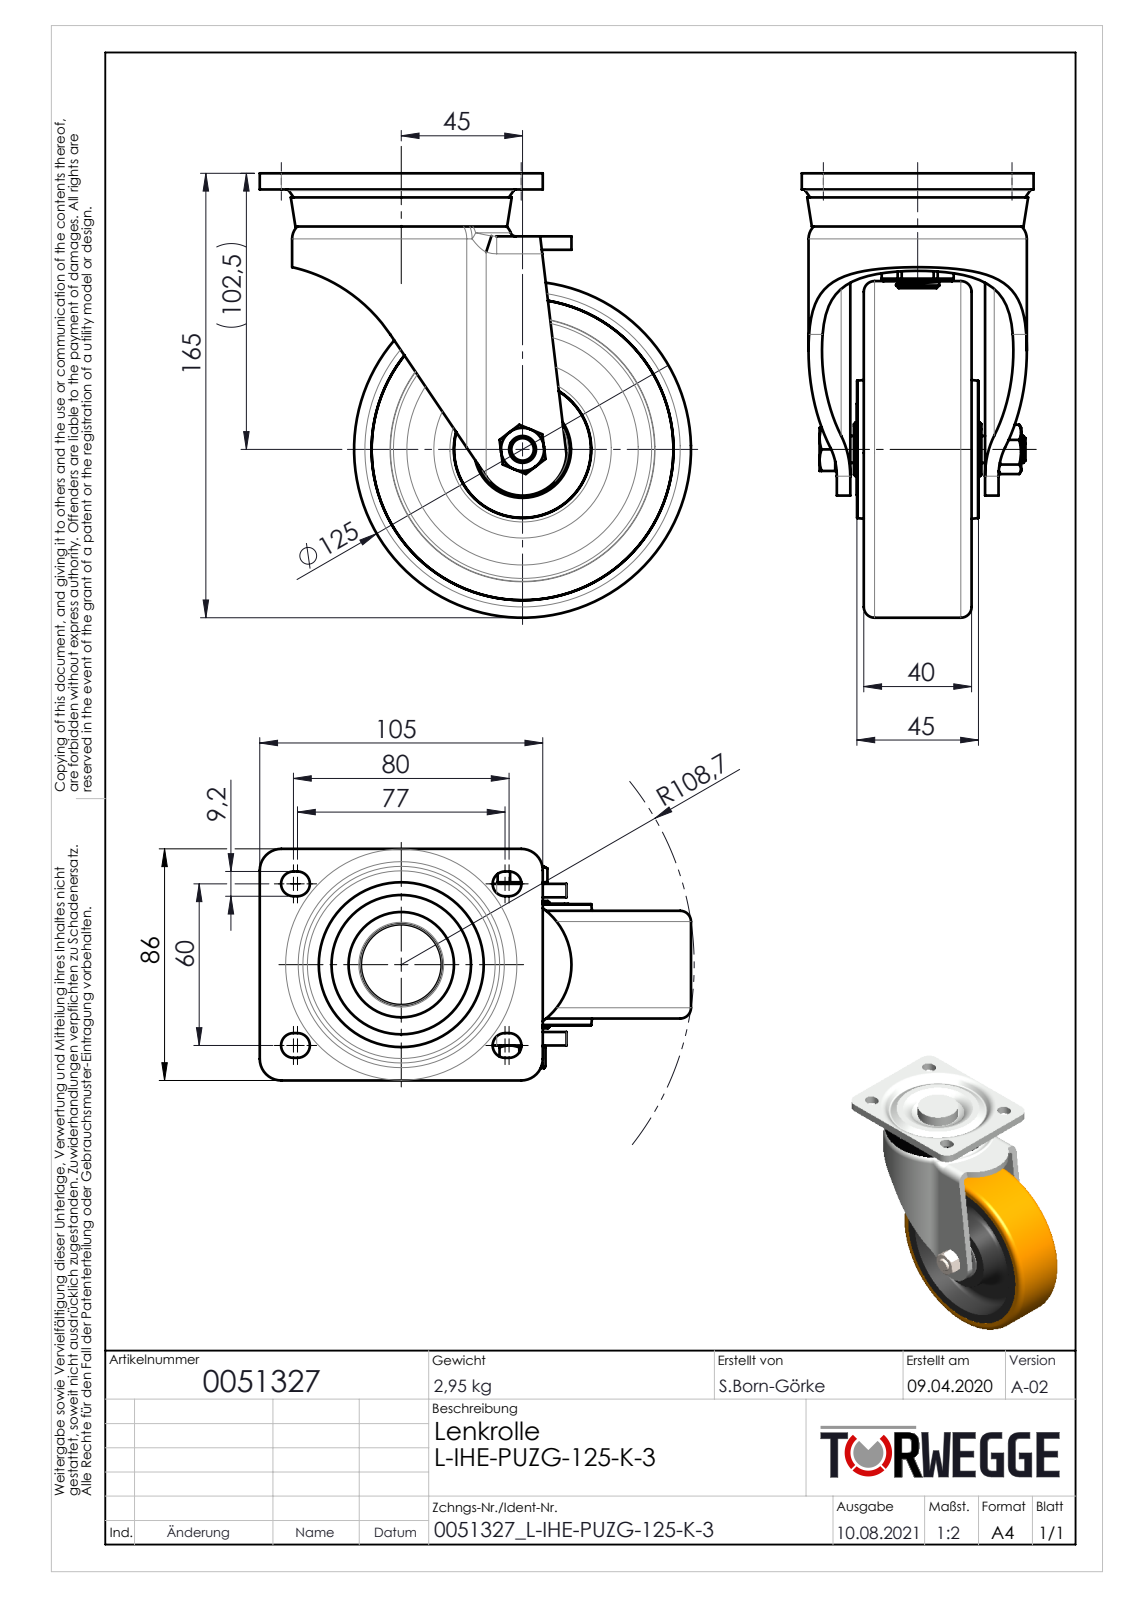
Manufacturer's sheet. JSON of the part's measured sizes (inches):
{"part_name": "0051327", "step_written_by": "SolidWorks 2020 (AUTOMOTIVE_DESIGN)", "units": "inches", "bodies": {"solids": 18, "faces": 739, "planar": 225, "cylindrical": 301, "other": 213}, "overall_size": [6.496, 6.299, 3.386], "volume_in3": 32.38, "surface_area_in2": 277.9, "round_holes": [[0.63, 2], [0.335, 1], [0.394, 1], [0.406, 1], [0.407, 1], [0.591, 1], [0.669, 1], [0.827, 1], [1.05, 1], [1.102, 1], [1.142, 1], [1.378, 1]], "round_bosses_or_shafts": [[4.921, 1], [2.787, 1], [2.48, 1], [2.31, 1], [1.181, 1], [0.866, 1], [0.778, 1], [0.587, 1]], "partial_cylinders_radius": [[0.02, 32], [0.181, 8], [0.315, 4], [0.059, 2], [0.256, 2], [0.472, 2], [0.644, 2], [0.669, 2]], "face_to_face_distances": [0.197, 1.969, 0.906, 1.772, 0.236, 0.669, 0.394, 1.063, 1.299, 1.102]}
